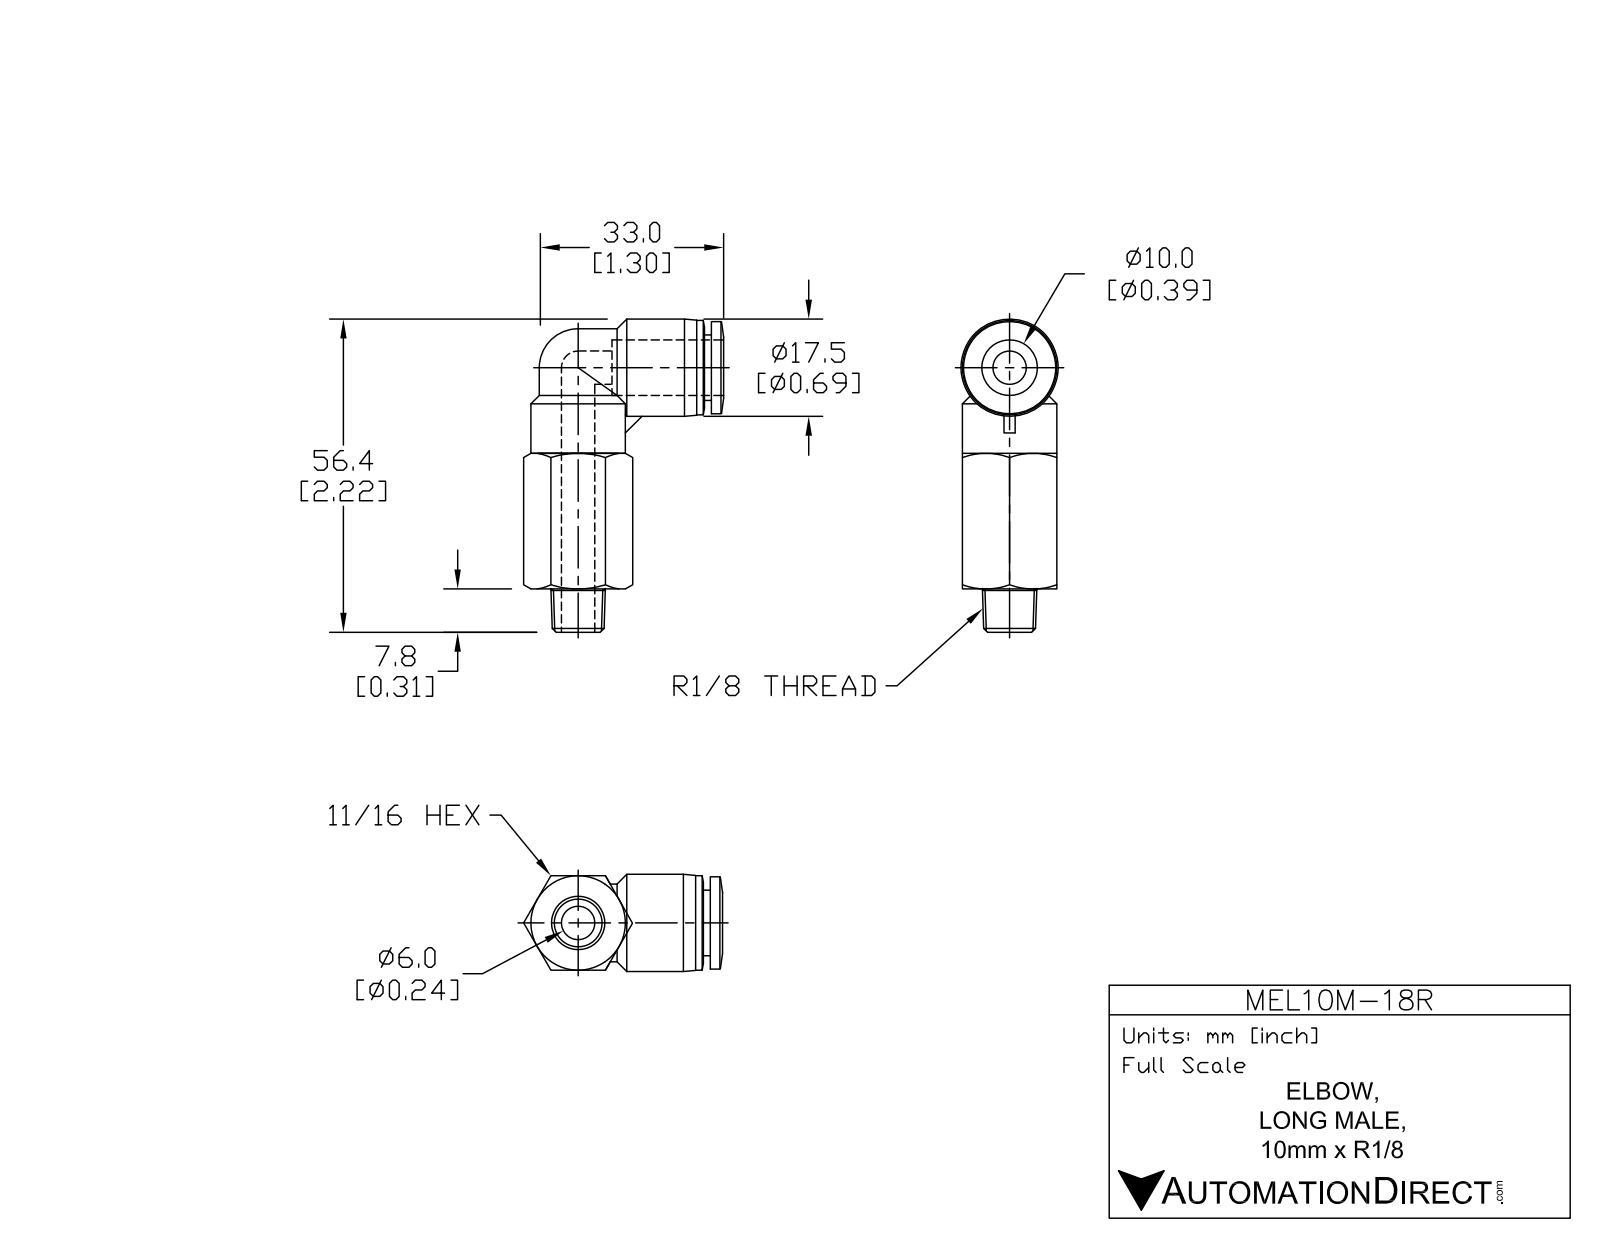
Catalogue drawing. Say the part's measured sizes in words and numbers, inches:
The part is named "MEL10M-18R". Its 3-D file was written by "SolidWorks 2015 (AUTOMOTIVE_DESIGN)". It is 1 solid with 69 faces: 16 planar, 20 cylindrical and 33 other. Overall it measures 2.222 by 1.355 by 0.689 inches. Its volume is 0.696 cubic inches and its surface area 9.113 square inches. Round holes: 2 of diameter 0.236, 1 of diameter 0.406. Round bosses or shafts: 2 of diameter 0.669, 1 of diameter 0.689, 1 of diameter 0.654, 1 of diameter 0.551, 1 of diameter 0.465. Partial cylindrical surfaces (rounded edges, fillets, slot ends): 1 of radius 0.276. The main face-to-face distances are 0.669, 0.049, 0.659, 0.709, 0.315, 0.295, 0.374, 0.079, 0.604, 0.055.
